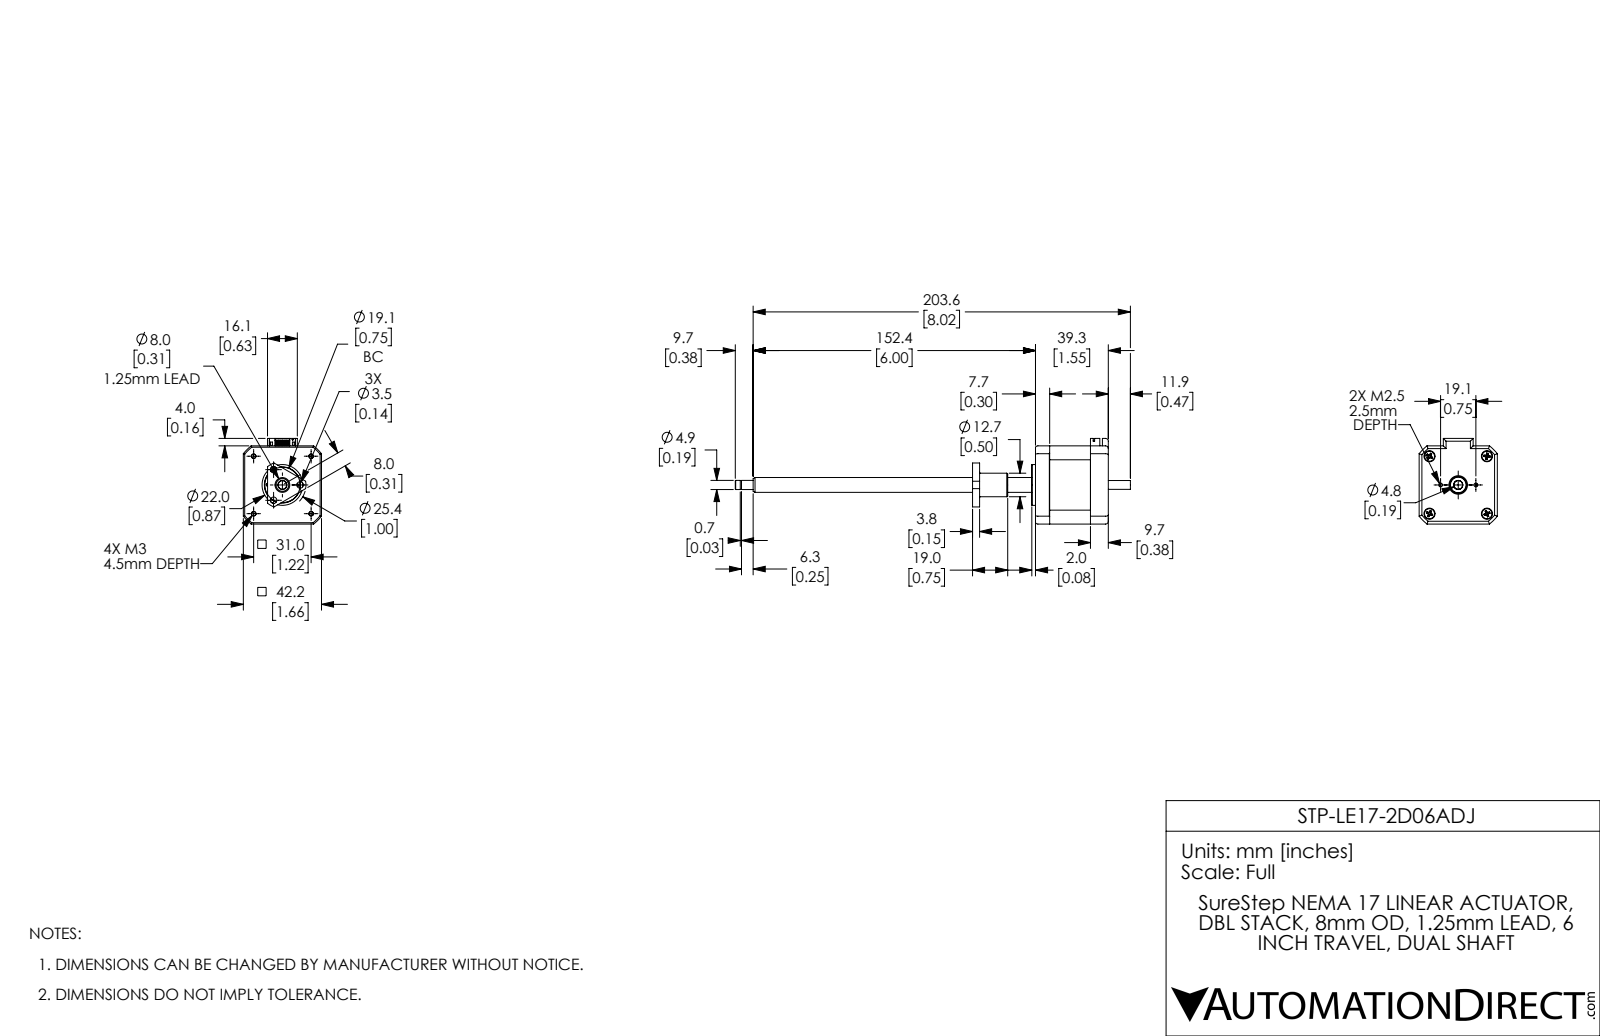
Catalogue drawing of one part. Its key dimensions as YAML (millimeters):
part_name: "STP-LE17-2D06ADJ; STP-LE17-2D06ADJ_1; STP-LE17-2D06ADJ_2"
step_written_by: "SolidWorks 2017 (AUTOMOTIVE_DESIGN)"
units: millimeters
bodies: {solids: 6, faces: 740, planar: 364, cylindrical: 240, other: 136}
overall_size: [213.25, 46.2, 42.2]
volume: 67931
surface_area: 29476
round_holes:
  - {diameter: 2.5, count: 4}
  - {diameter: 3.8, count: 4}
  - {diameter: 6, count: 4}
  - {diameter: 3.5, count: 3}
  - {diameter: 1.5, count: 2}
  - {diameter: 2.05, count: 2}
  - {diameter: 4.9, count: 1}
  - {diameter: 5, count: 1}
  - {diameter: 10, count: 1}
  - {diameter: 13, count: 1}
  - {diameter: 17, count: 1}
  - {diameter: 19.46, count: 1}
round_bosses_or_shafts:
  - {diameter: 5.4, count: 4}
  - {diameter: 2.91, count: 4}
  - {diameter: 27, count: 1}
  - {diameter: 25.91, count: 1}
  - {diameter: 22, count: 1}
  - {diameter: 12.7, count: 1}
  - {diameter: 12, count: 1}
  - {diameter: 9, count: 1}
partial_cylinders:
  - {radius: 1, count: 12}
  - {radius: 1.5, count: 11}
  - {radius: 2.5, count: 2}
  - {radius: 0.7, count: 1}
  - {radius: 12.7, count: 1}
  - {radius: 14.25, count: 1}
  - {radius: 16, count: 1}
  - {radius: 25.1, count: 1}
face_to_face_distances: [42.2, 9.65, 39.3, 29.65, 31.65, 1.6, 22, 7.65, 1, 36.8]
hole_center_spacings: [16.61, 9.52, 21.92, 29.43, 31, 4.93, 8, 12.96]
